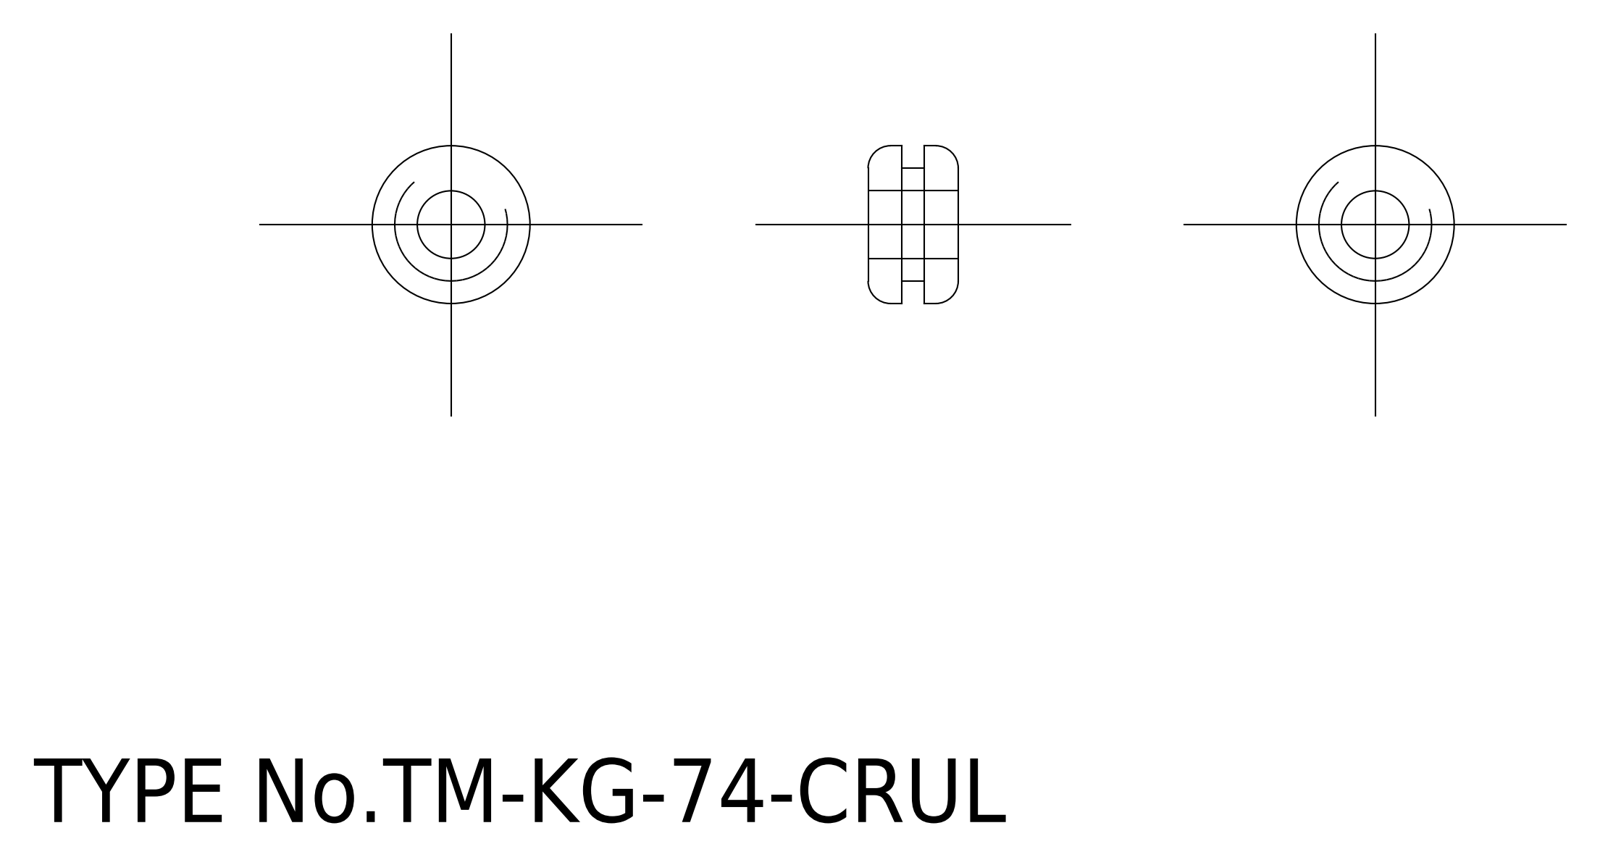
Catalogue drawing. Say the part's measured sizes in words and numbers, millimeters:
Its 3-D file was written by "spGate 15.6.1 (AUTOMOTIVE_DESIGN)". It is 1 solid with 16 faces: 4 planar, 8 cylindrical and 4 other. Overall it measures 7 by 7 by 4 millimeters. Its volume is 98 cubic millimeters and its surface area 200 square millimeters. Round holes: 1 of diameter 3. Round bosses or shafts: 1 of diameter 7, 1 of diameter 5. The main face-to-face distances are 1.5, 2.5, 1, 4.
